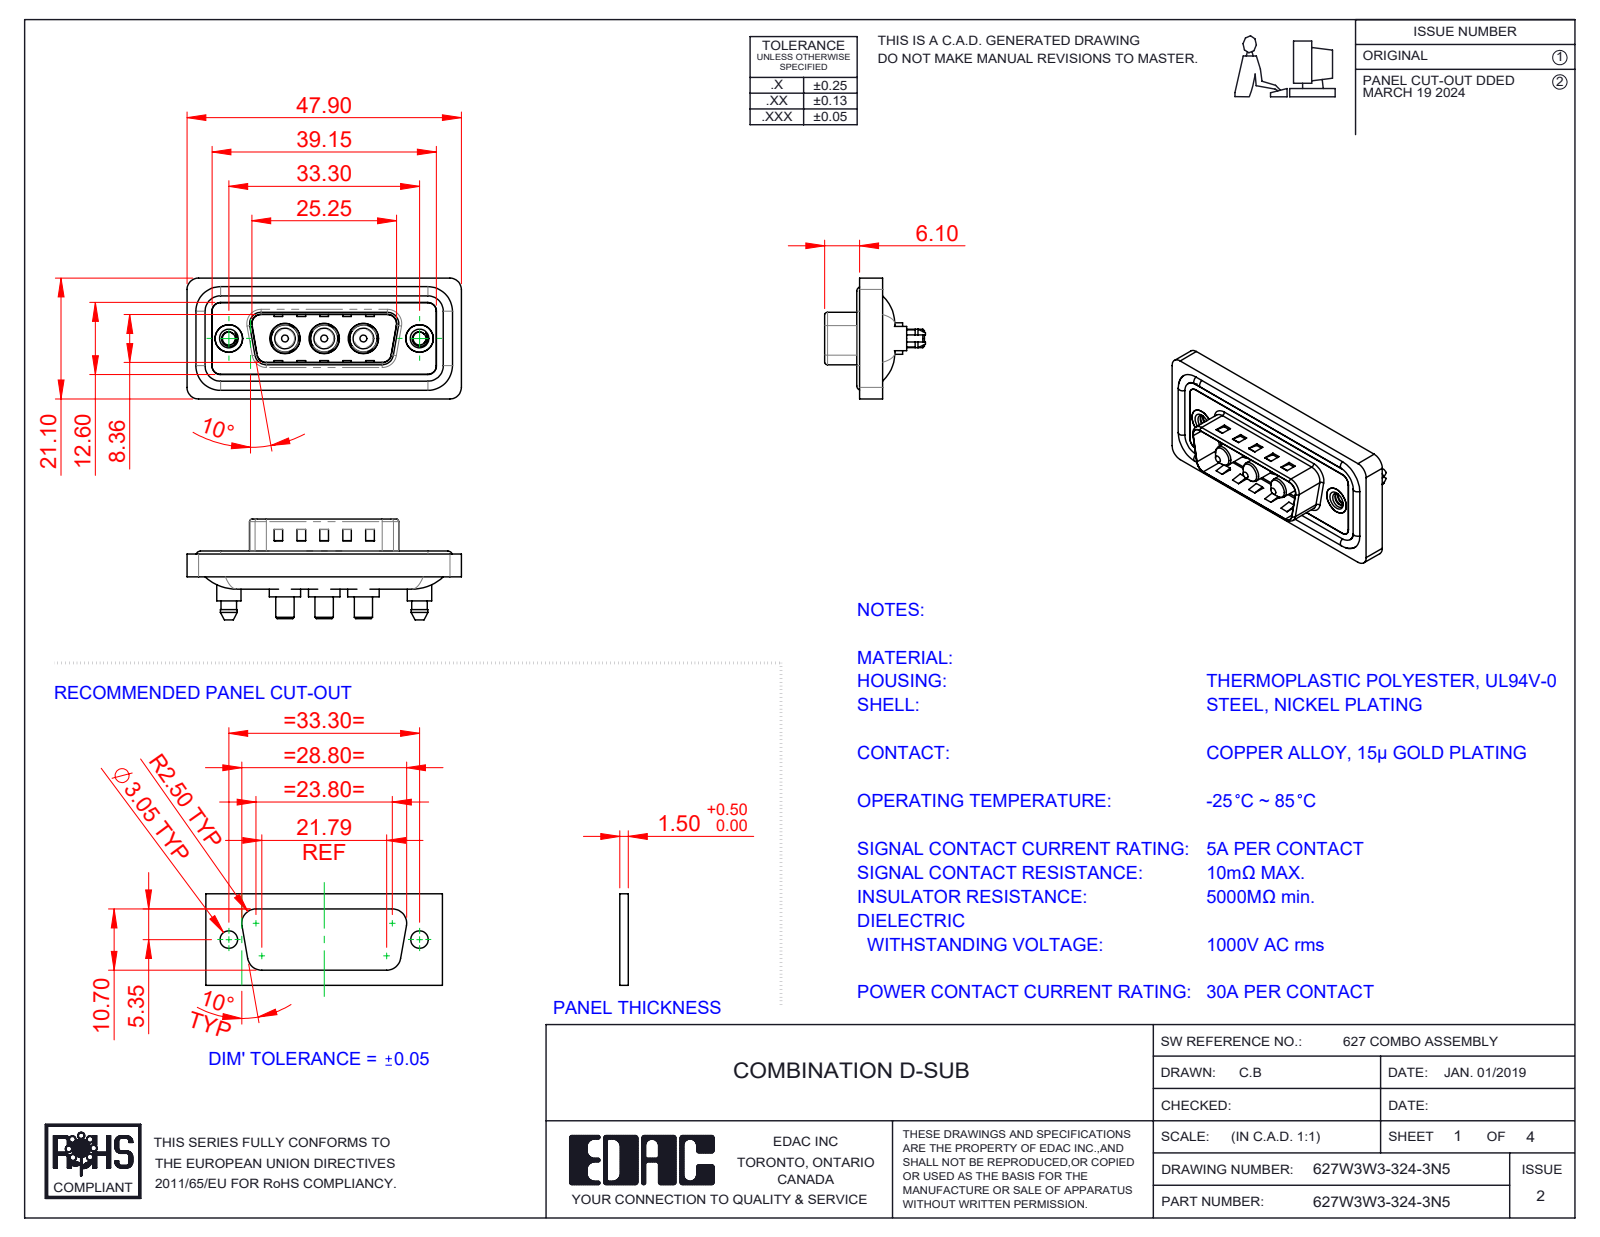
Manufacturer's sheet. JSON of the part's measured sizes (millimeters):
{"part_name": "Power Pin_30A S; 627Combo Housing_3W3; 627Combo Shell Rear_15 Contacts; 627Combo Threaded Boardlock_5 (+3 more)", "step_written_by": "SolidWorks 2023 (CONFIG_CONTROL_DESIGN)", "units": "millimeters", "bodies": {"solids": 13, "faces": 614, "planar": 223, "cylindrical": 273, "other": 118}, "overall_size": [47.9, 21.1, 17.6], "volume_mm3": 5741, "surface_area_mm2": 9100, "round_holes": [[4.85, 3], [5.3, 3], [2.26, 2], [4, 2], [4.8, 2], [5, 2]], "round_bosses_or_shafts": [[1.6, 4], [5.5, 3], [5.2, 3], [4.75, 3], [3.75, 3], [3.6, 3], [3.2, 3], [5.4, 2]], "partial_cylinders_radius": [[1.5, 28], [2, 20], [1.6, 10], [0.5, 8], [0.25, 4], [0.6, 4], [0.65, 4], [0.9, 4]], "face_to_face_distances": [0.4, 1.1, 1.5, 3.1, 1.6, 0.5, 2.9, 4, 0.7, 0.82], "hole_center_spacings": [6.85, 9.8, 16.65, 23.5, 13.7, 33.3]}
